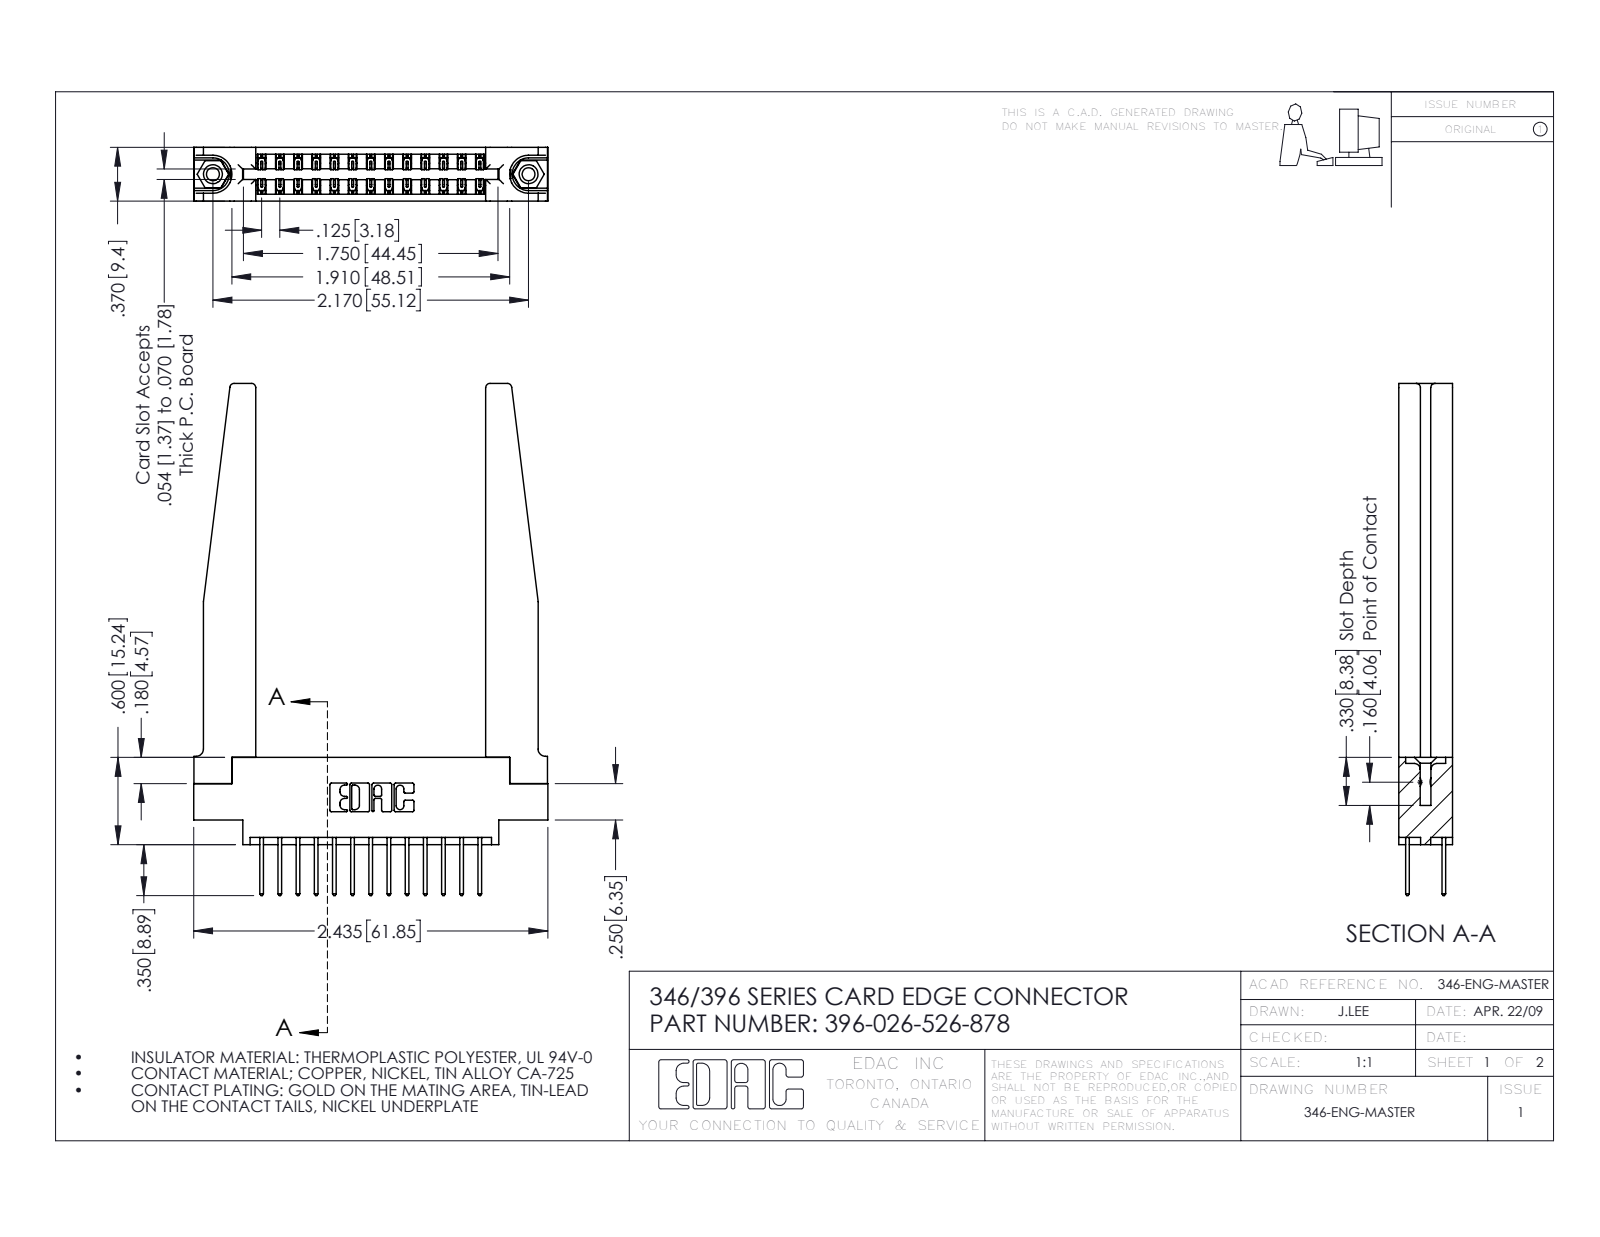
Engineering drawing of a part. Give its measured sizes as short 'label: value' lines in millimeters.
name: 396-026-526-878; 345-250-001_345-250-001-102; 346-220-078_345-220-078; 346 Part_0.170 Offset - 0.156 Dia-TH (+1 more)
written by: SolidWorks 2016 (CONFIG_CONTROL_DESIGN)
unit: mm
bodies: 31 solids, 1712 faces (1132 planar, 528 cylindrical, 52 other)
size: 89.4 × 61.8 × 9.4
volume: 12 600 mm³; area: 14 280 mm²
holes: 2× ⌀2.3, 2× ⌀3.2, 2× ⌀4, 1× ⌀1.6
bosses: 2× ⌀3.9
rounds: 39× R0.2, 26× R0.3, 22× R0.3, 8× R0.8, 6× R0.2, 6× R0.8, 3× R0.7, 2× R0.4
face distances: 9.4, 1.8, 3.8, 3.8, 1.2, 8.2, 6.4, 7.6, 0.6, 2.6
hole spacings: 6.2, 49.9, 55.1
